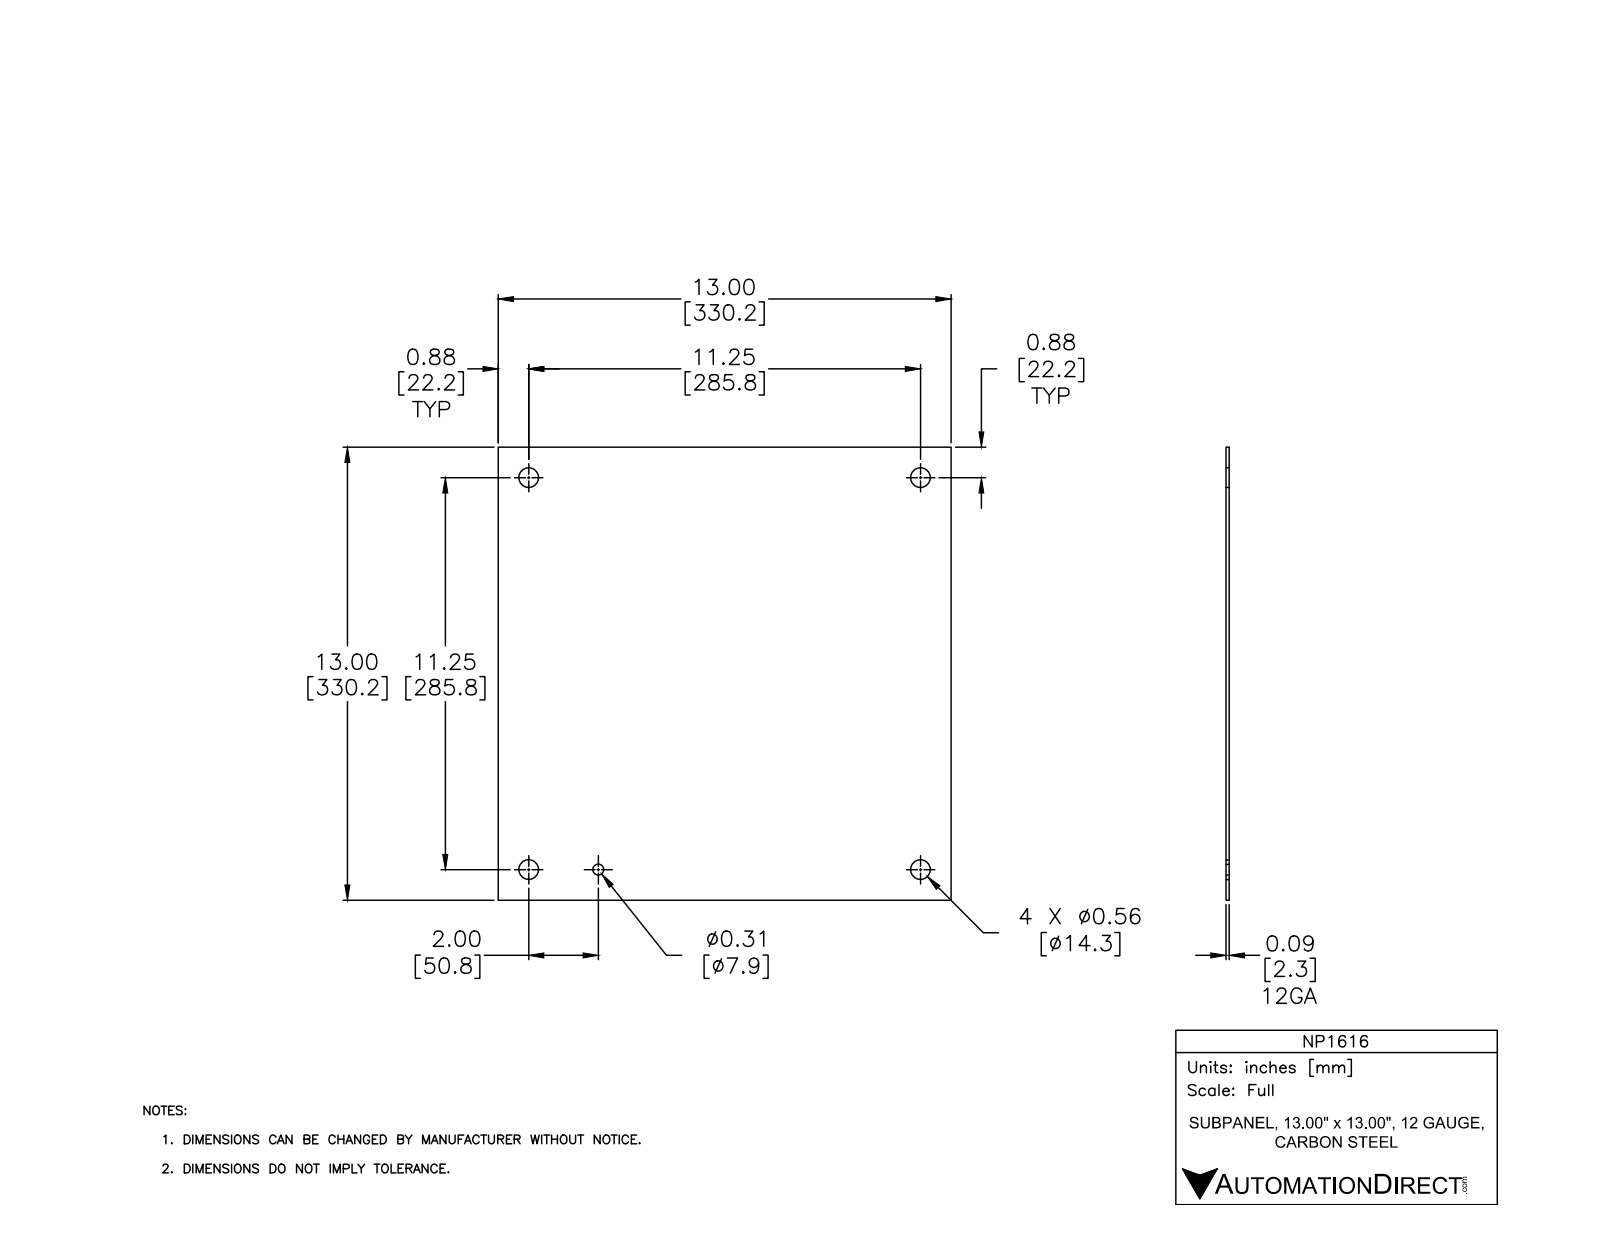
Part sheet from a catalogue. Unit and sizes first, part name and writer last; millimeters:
Units: millimetres
Overall size (bounding box): 330.2 × 330.2 × 2.4
Round holes (diameter × count): ⌀14.3 ×4, ⌀7.9 ×1
Main face-to-face distances: 2.4, 330.2
Hole centre spacings: 285.8, 50.8, 235, 285.8, 290.2, 370, 404.1, 404.1
Volume: 257 900 mm³ · Surface area: 220 300 mm²
Bodies: 1 solid, 11 faces (6 planar, 5 cylindrical, 0 other)
Part name (STEP PRODUCT): NP1616
STEP written by: Autodesk Inventor 2012 (AUTOMOTIVE_DESIGN)
